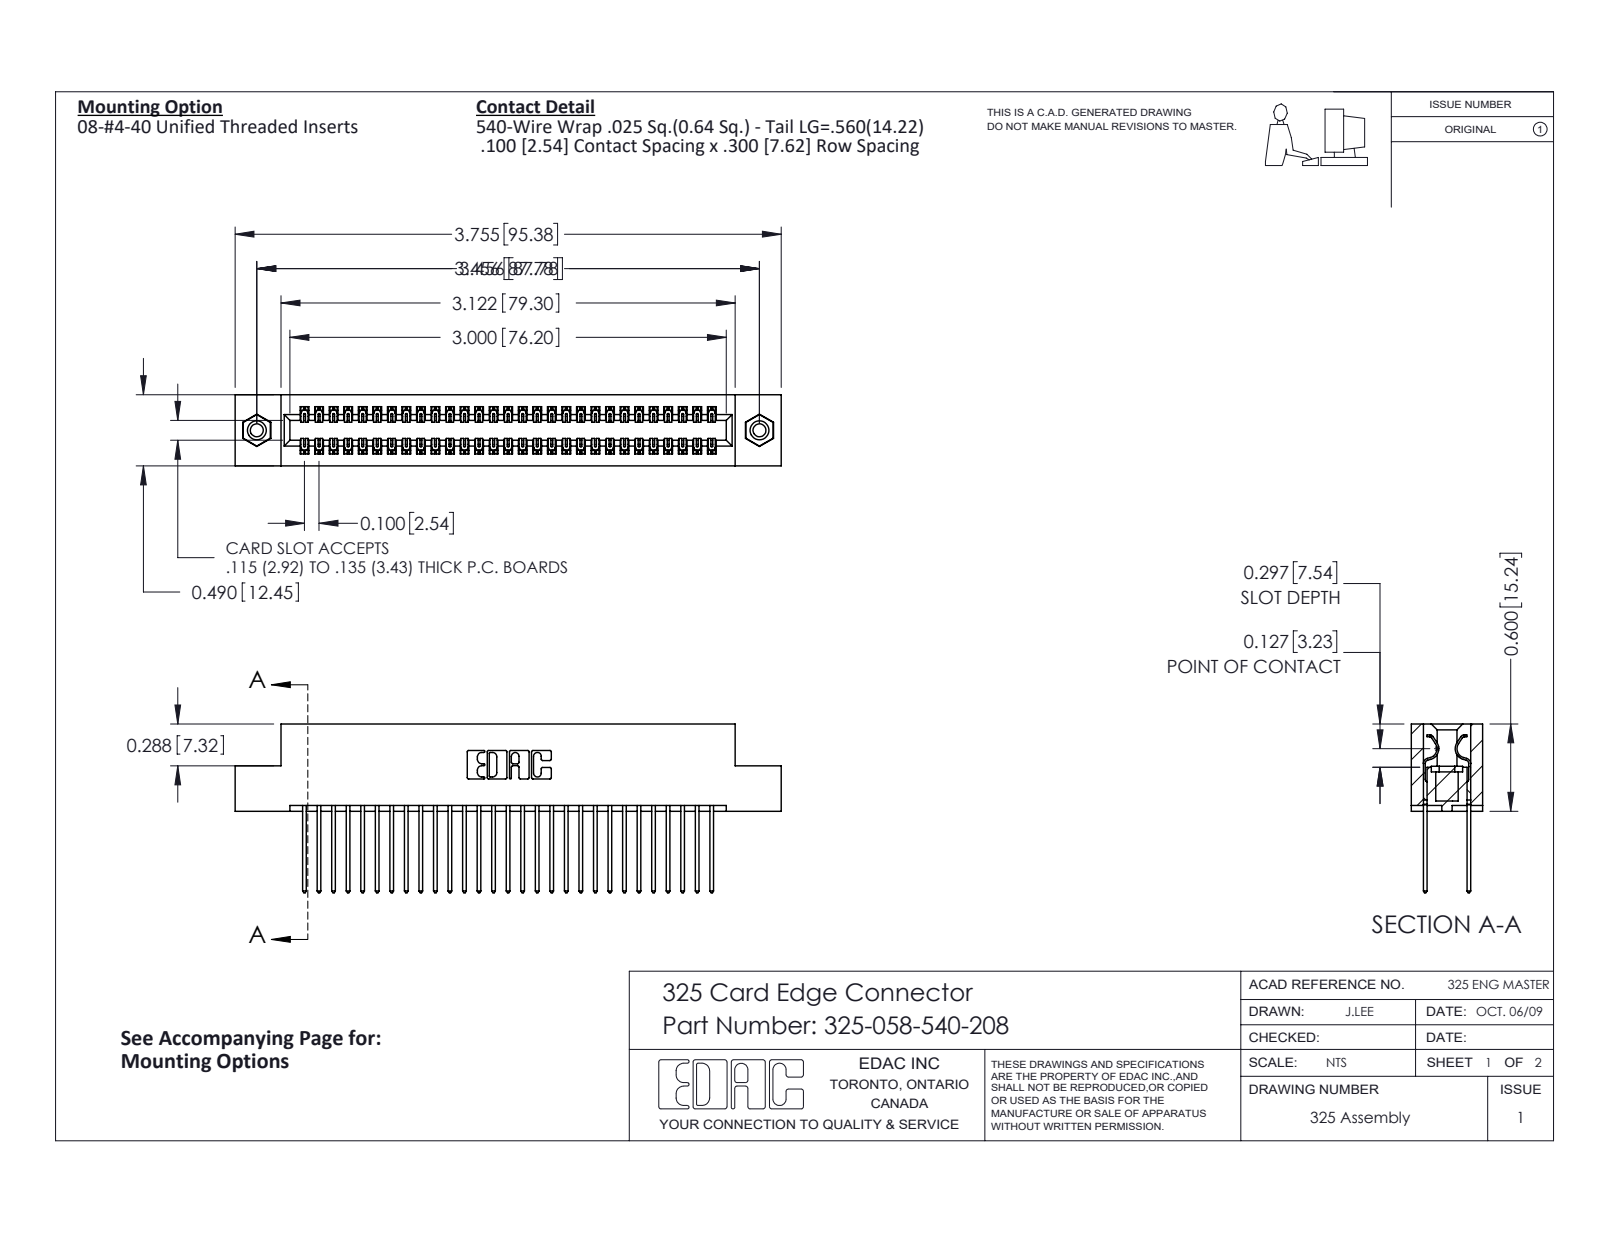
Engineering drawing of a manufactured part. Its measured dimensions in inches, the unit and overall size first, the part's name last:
Units: inches
Overall size (bounding box): 3.755 × 1.16 × 0.49
Round holes (diameter × count): ⌀0.089 ×2, ⌀0.125 ×2, ⌀0.16 ×2
Round bosses / shafts (diameter × count): ⌀0.155 ×2
Partial cylindrical surfaces — rounded edges, fillets, slot ends (radius × count): R0.006 ×87, R0.01 ×58, R0.01 ×22, R0.007 ×6, R0.031 ×6, R0.026 ×3, R0.014 ×2, R0.022 ×2
Main face-to-face distances: 0.083, 0.407, 0.3, 0.107, 0.383, 0.025, 0.49, 0.325, 0.275, 0.04
Hole centre spacings: 3.456
Volume: 0.757 in³ · Surface area: 24.45 in²
Bodies: 61 solids, 3190 faces (2190 planar, 984 cylindrical, 16 other)
Part name (STEP PRODUCT): 325-058-540-208; 325-292-001_325-293-140; 345-250-001_345-250-003-102; 325 Part_TI
STEP written by: SolidWorks 2016 (CONFIG_CONTROL_DESIGN)
